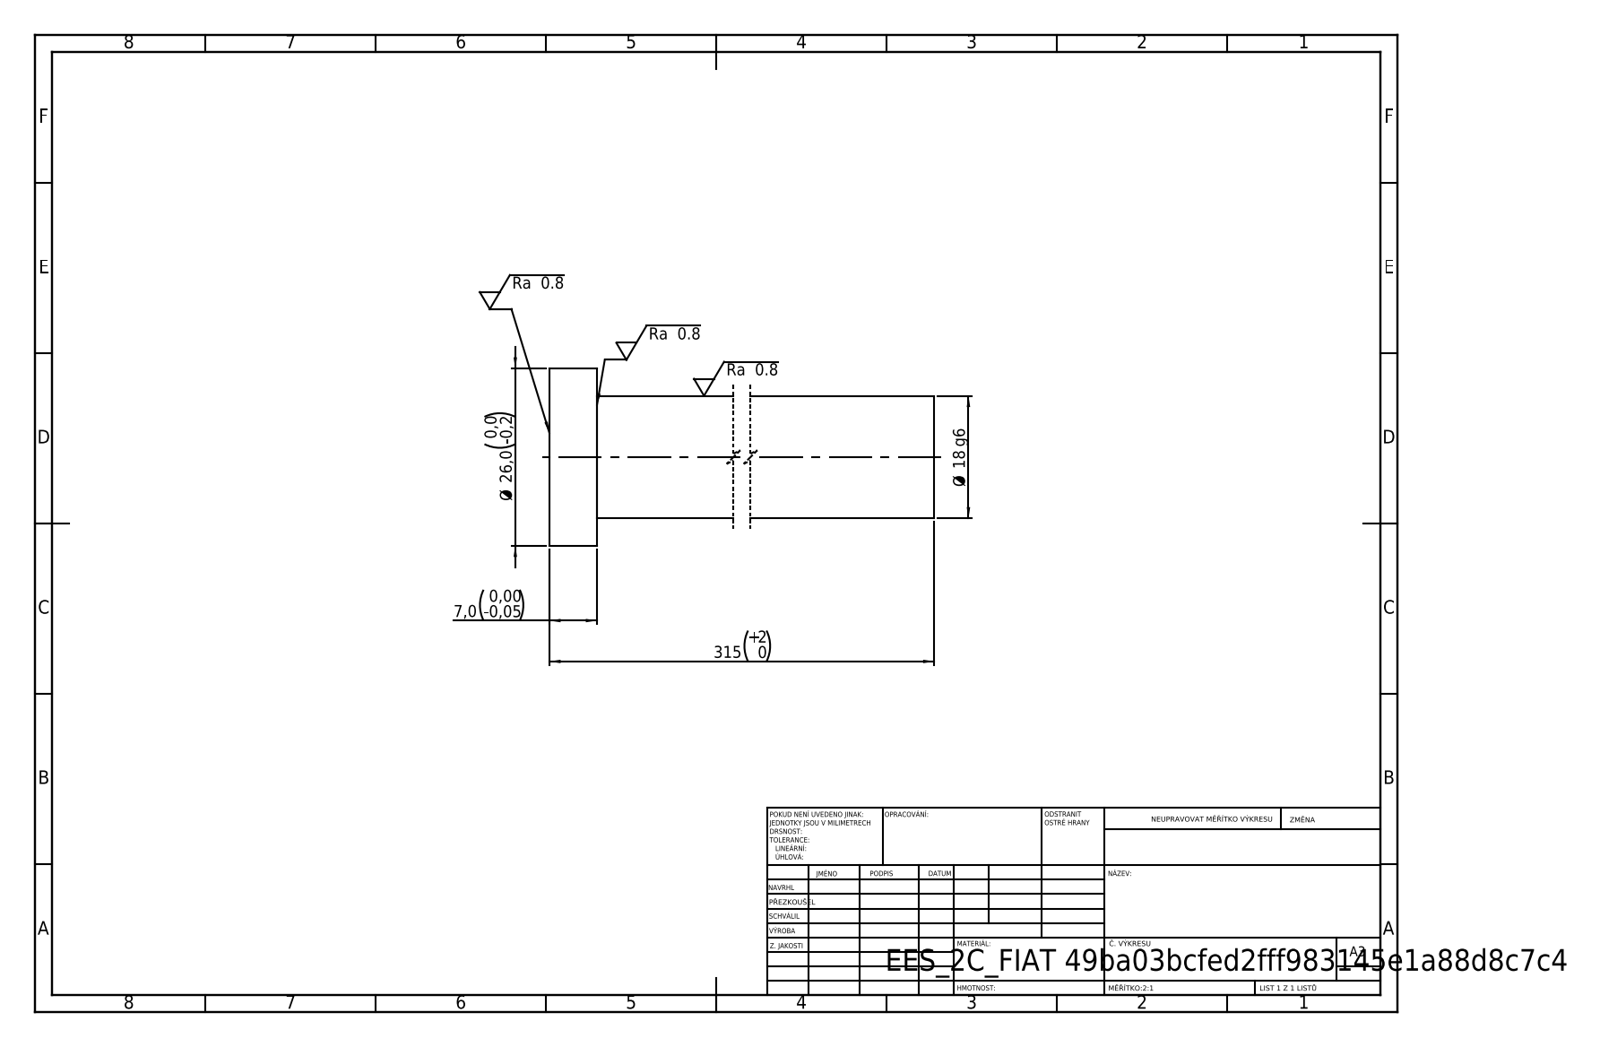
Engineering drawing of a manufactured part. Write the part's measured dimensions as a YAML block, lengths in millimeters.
step_written_by: "SolidWorks 2019 (CONFIG_CONTROL_DESIGN)"
units: millimeters
bodies: {solids: 1, faces: 7, planar: 3, cylindrical: 4, other: 0}
overall_size: [315, 26, 26]
volume: 82093
surface_area: 19051
round_bosses_or_shafts:
  - {diameter: 26, count: 1}
  - {diameter: 18, count: 1}
face_to_face_distances: [7, 315, 308]
